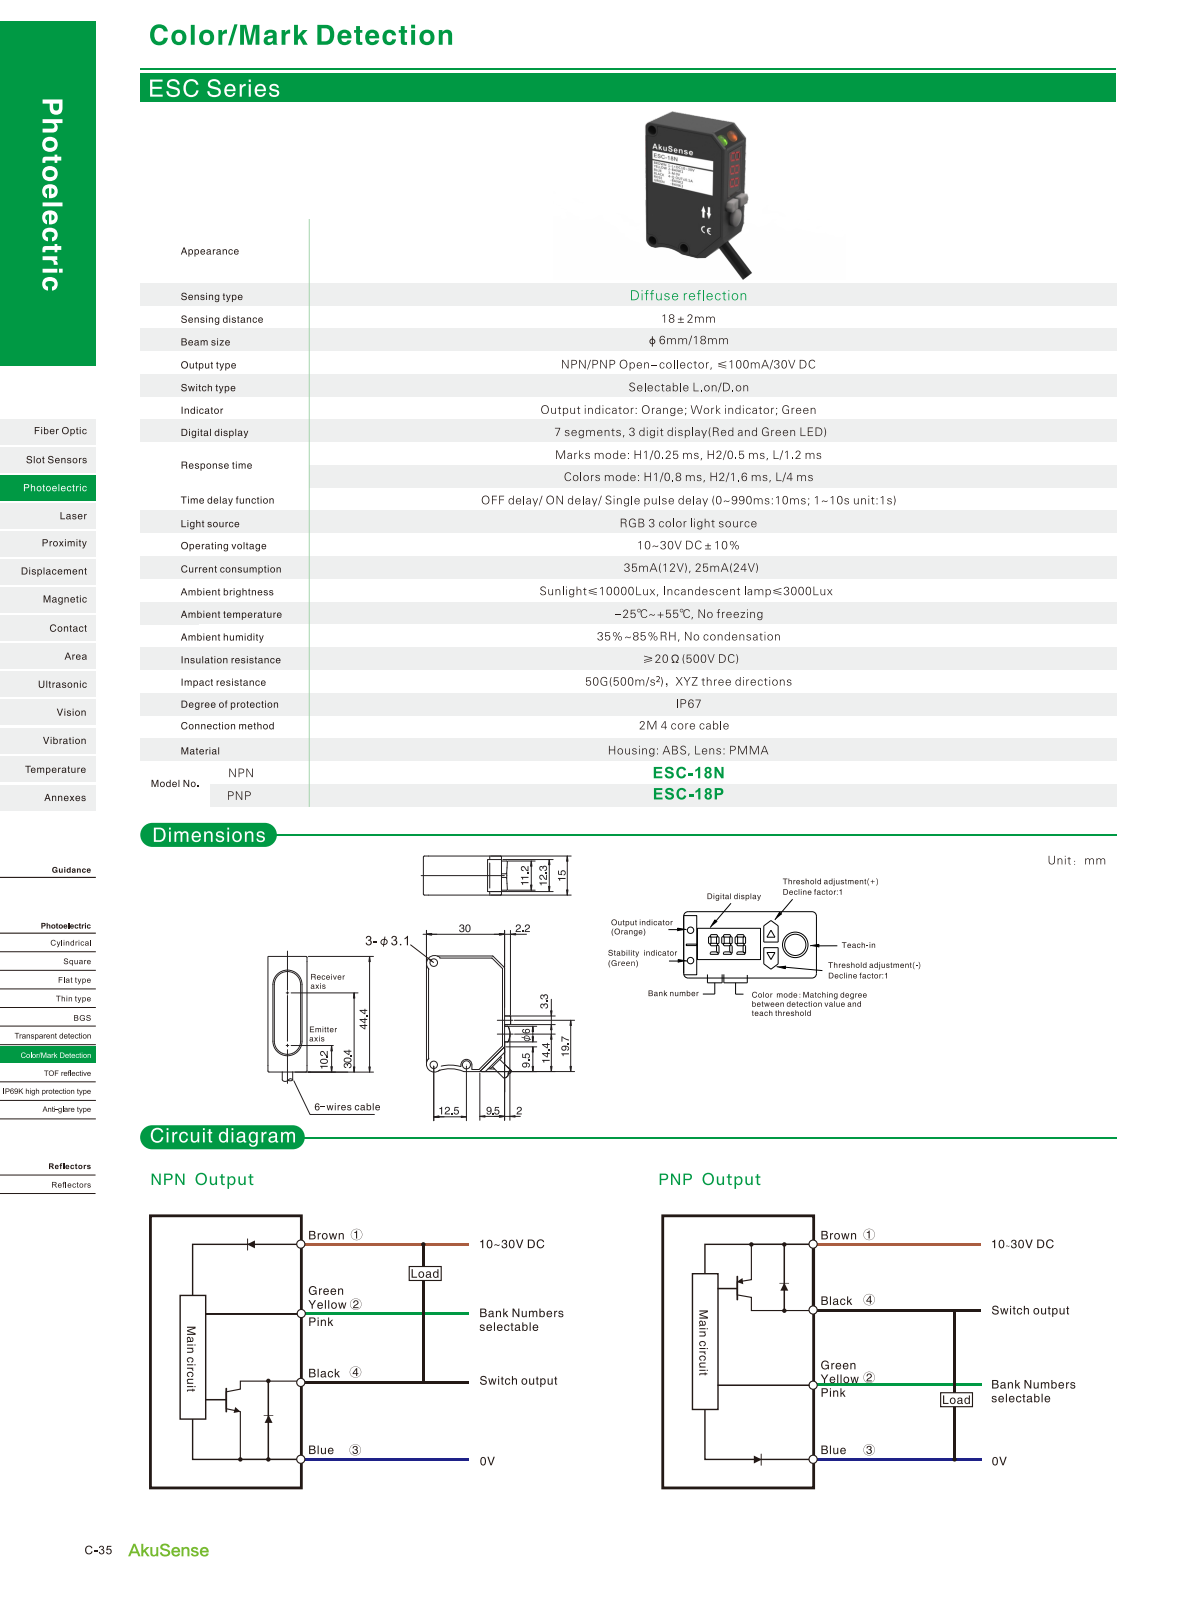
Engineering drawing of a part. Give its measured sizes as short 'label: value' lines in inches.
name: ESC-18N
written by: SolidWorks 2013 (AUTOMOTIVE_DESIGN)
unit: in
bodies: 1 solid, 398 faces (105 planar, 137 cylindrical, 156 other)
size: 2.03 × 1.463 × 0.591
volume: 1.16 in³; area: 8.922 in²
holes: 3× ⌀0.122
bosses: 1× ⌀0.236, 1× ⌀0.157
rounds: 50× R0.004, 24× R0.008, 18× R0.016, 10× R0.006, 3× R0.083, 3× R0.085, 2× R0.02, 2× R0.219
face distances: 0.587, 0.591, 1.181, 0.031, 1.179, 1.748, 0.033, 1.148, 1.15, 1.116
hole spacings: 0.494, 1.545, 1.622
